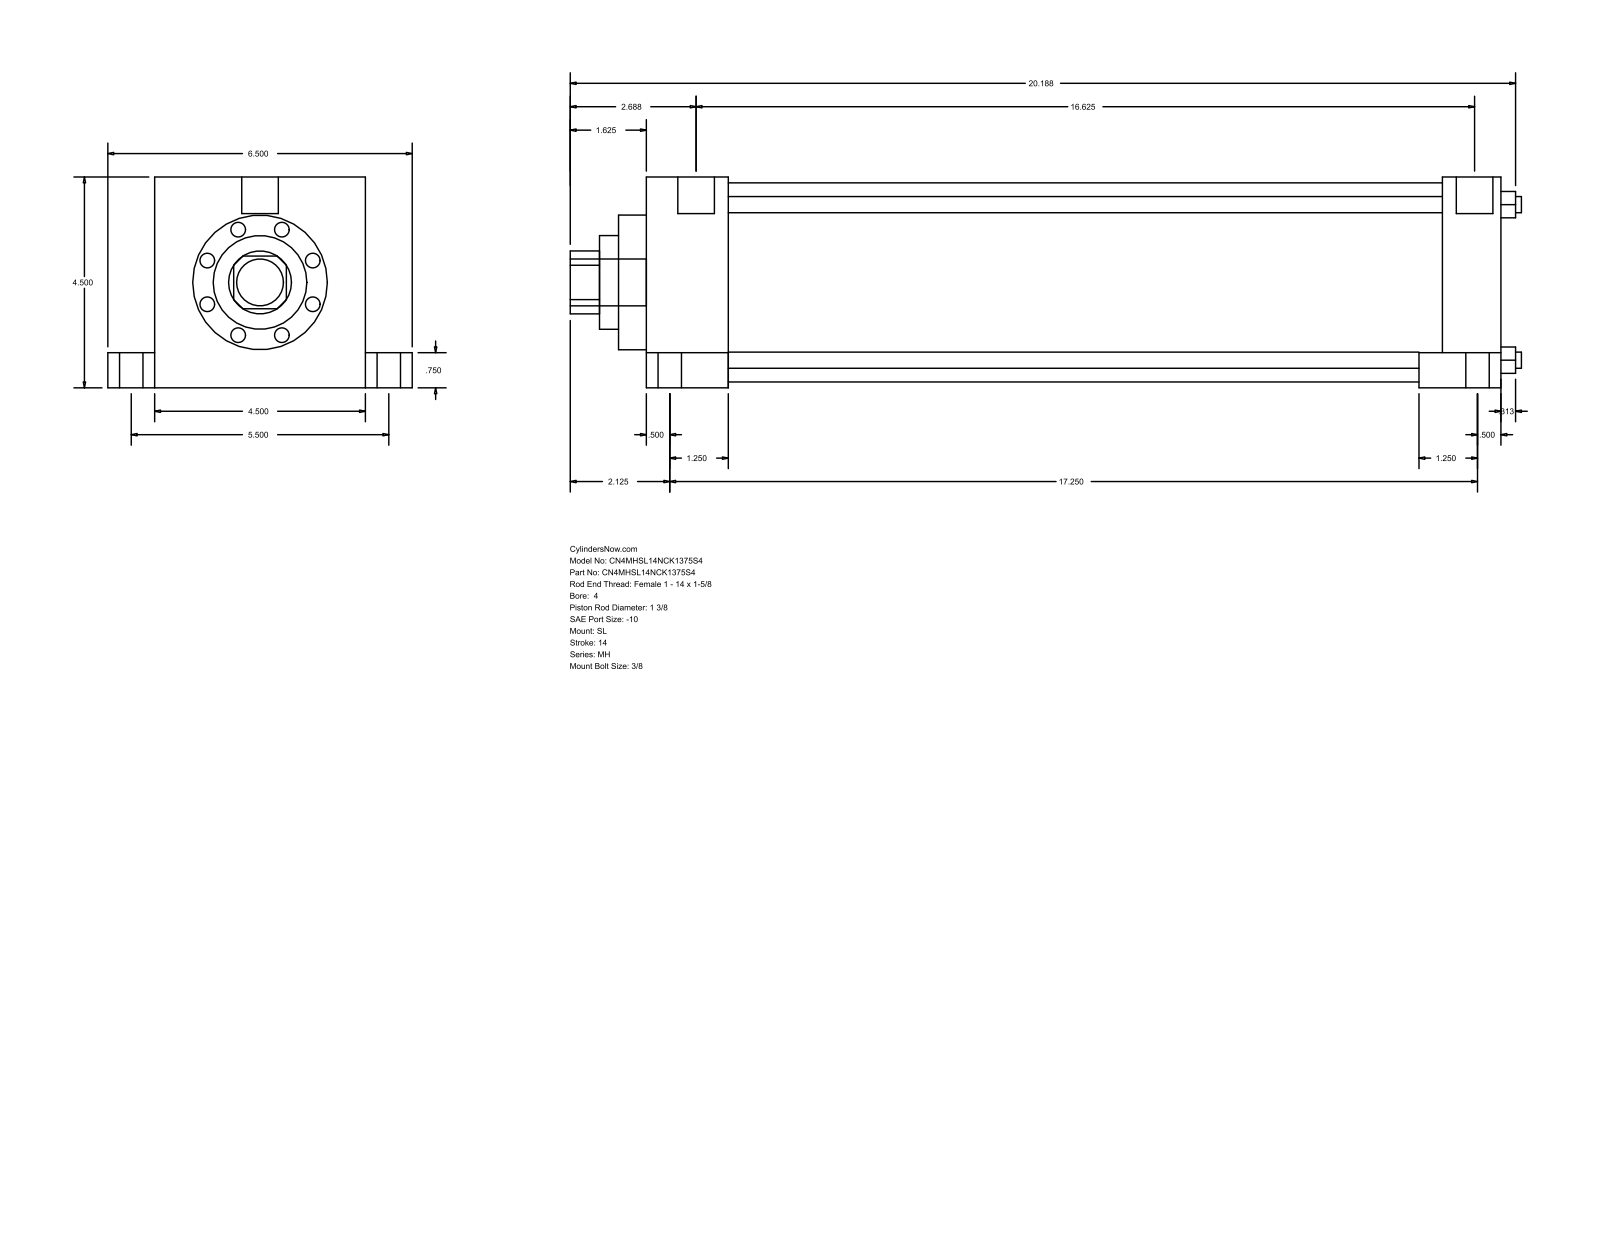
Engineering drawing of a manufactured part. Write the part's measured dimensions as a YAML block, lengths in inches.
part_name: "MH_SL__0400_1.375"
step_written_by: "GSSL Pune (CONFIG_CONTROL_DESIGN)"
units: inches
bodies: {solids: 0, faces: 110, planar: 77, cylindrical: 33, other: 0}
overall_size: [20.313, 6.5, 4.5]
round_holes:
  - {diameter: 0.345, count: 4}
  - {diameter: 1.375, count: 1}
  - {diameter: 2, count: 1}
  - {diameter: 2.875, count: 1}
  - {diameter: 4.25, count: 1}
round_bosses_or_shafts:
  - {diameter: 0.75, count: 4}
  - {diameter: 0.5, count: 4}
  - {diameter: 0.344, count: 4}
  - {diameter: 0.781, count: 2}
  - {diameter: 1, count: 1}
partial_cylinders:
  - {radius: 0.672, count: 1}
face_to_face_distances: [4.5, 18.25, 1.75, 16.5, 17, 15.25, 1.25, 1, 5.5, 0.75]
hole_center_spacings: [2.347, 3.32, 4.695]
